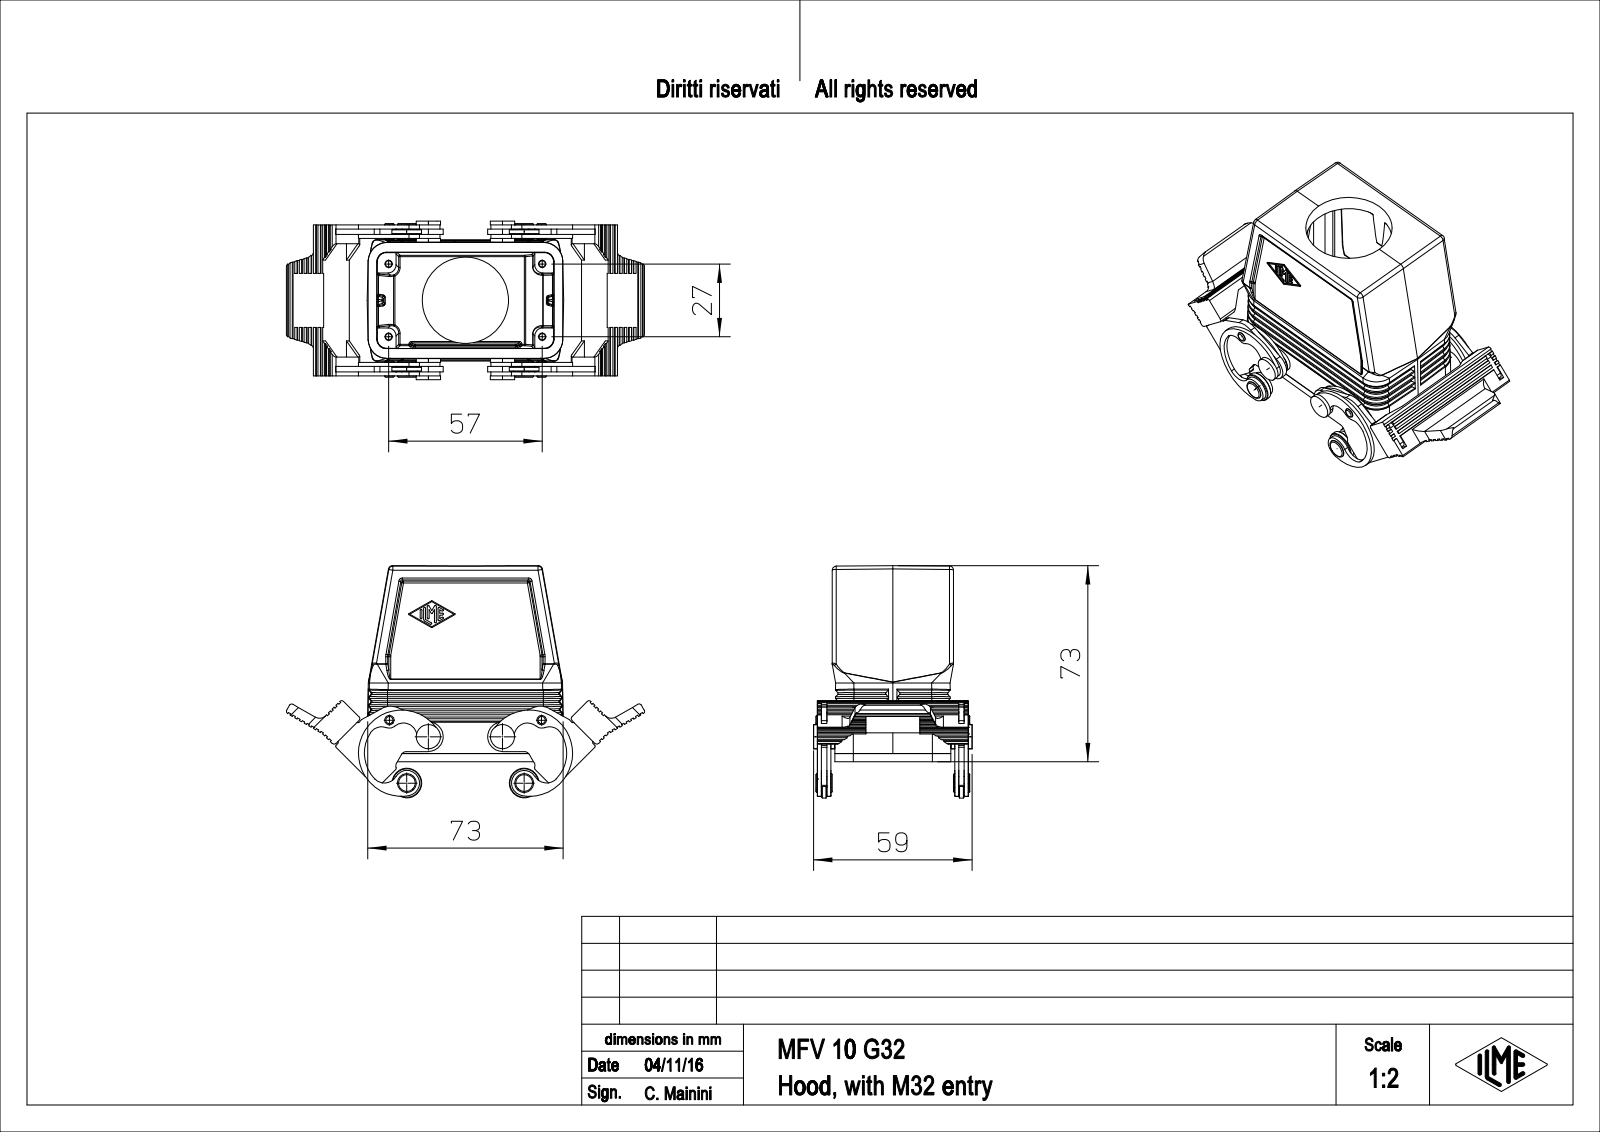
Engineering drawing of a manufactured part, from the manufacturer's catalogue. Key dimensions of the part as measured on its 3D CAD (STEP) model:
Part name (STEP PRODUCT): CAV Tüllengehäuse 2 Bügel für einen Einsatz
STEP written by: Autodesk Inventor 7 (AUTOMOTIVE_DESIGN)
Units: millimetres
Bodies: 1 solid, 832 faces (255 planar, 222 cylindrical, 355 other)
Overall size (bounding box): 115.79 × 98.08 × 58
Volume: 85 290 mm³ · Surface area: 50 001 mm²
Round holes (diameter × count): ⌀2.5 ×2, ⌀32 ×1
Round bosses / shafts (diameter × count): ⌀11 ×2, ⌀9 ×2, ⌀5 ×2, ⌀2 ×2
Partial cylindrical surfaces — rounded edges, fillets, slot ends (radius × count): R0.25 ×14, R1 ×12, R2.5 ×10, R6 ×10, R3 ×8, R2 ×7, R3.5 ×4, R5 ×4
Main face-to-face distances: 4, 3, 39, 38, 35, 1, 42, 43, 41, 2
Hole centre spacings: 50.2
